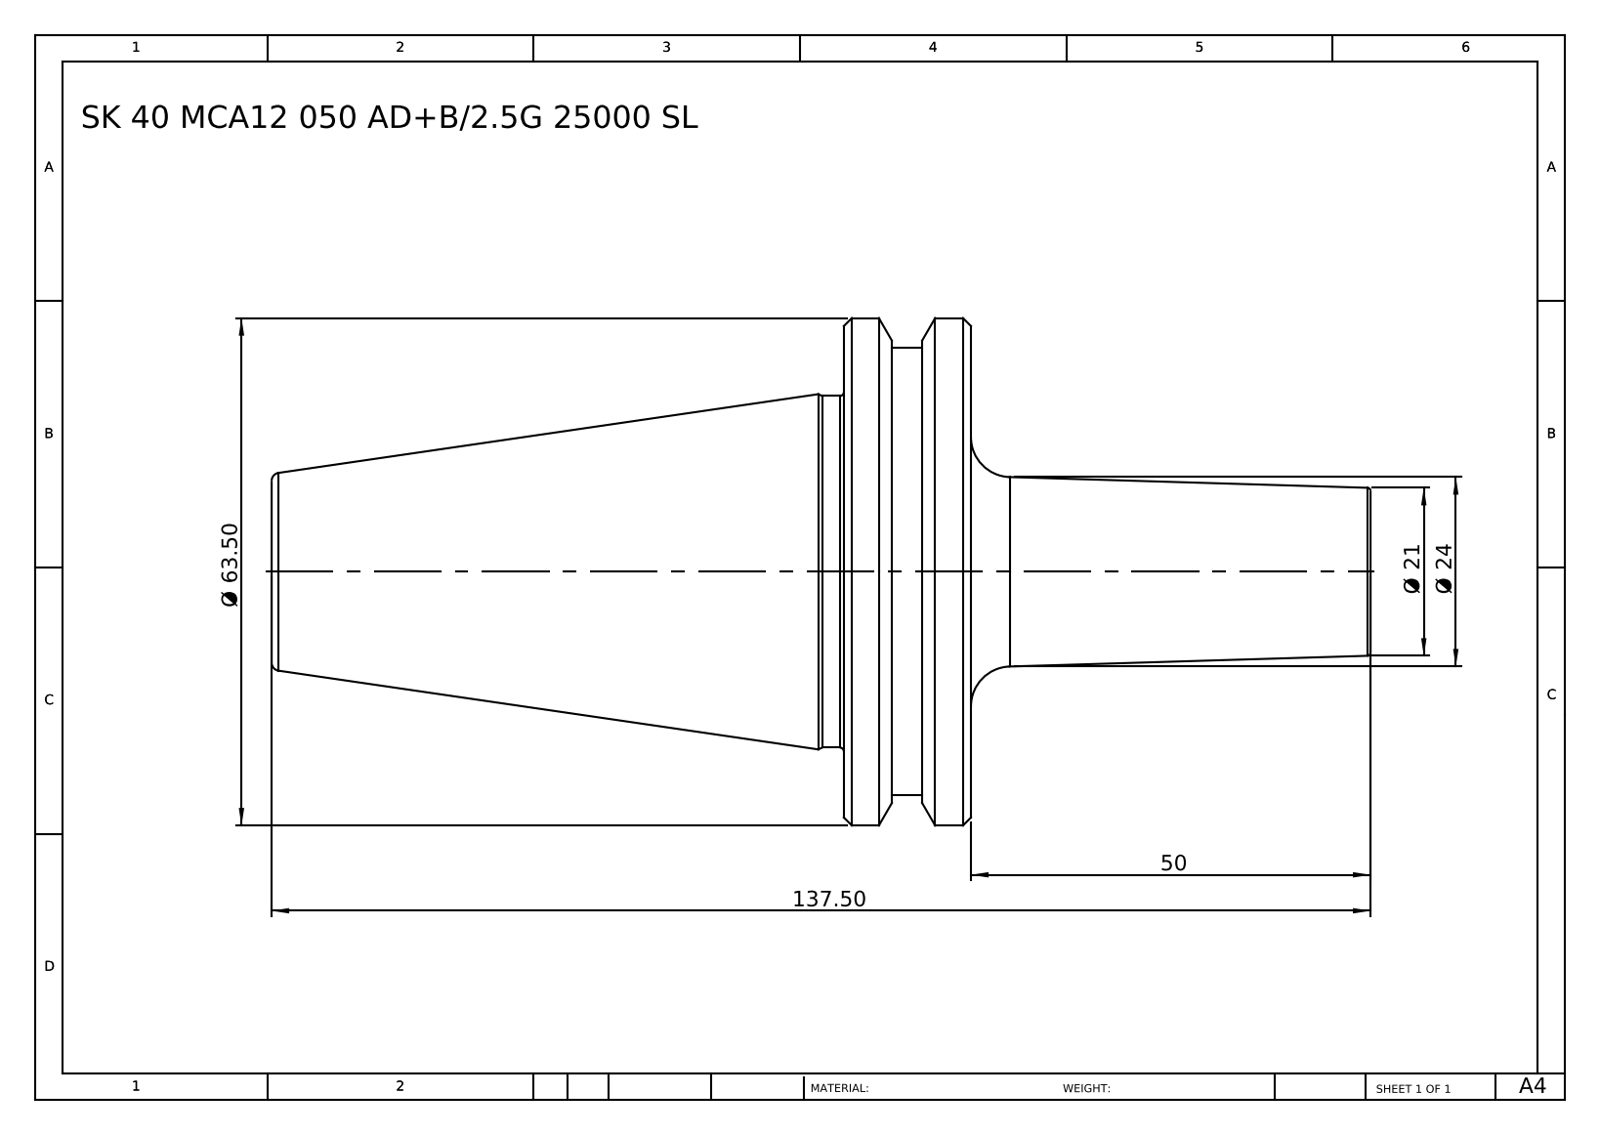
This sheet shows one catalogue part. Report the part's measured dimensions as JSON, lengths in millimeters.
{"part_name": "SK 40 MCA12 050 AD+B-2.5G 25000 SL", "step_written_by": "SolidWorks 2014 (CONFIG_CONTROL_DESIGN)", "units": "millimeters", "bodies": {"solids": 1, "faces": 36, "planar": 6, "cylindrical": 8, "other": 22}, "overall_size": [137.5, 63.5, 63.5], "volume_mm3": 137424, "surface_area_mm2": 20221, "round_bosses_or_shafts": [[63.5, 1], [56, 1], [44, 1]], "face_to_face_distances": [15.9, 87.5, 71.6, 50, 65.9, 137.5, 56.1, 6.1, 9.8, 81.4]}
